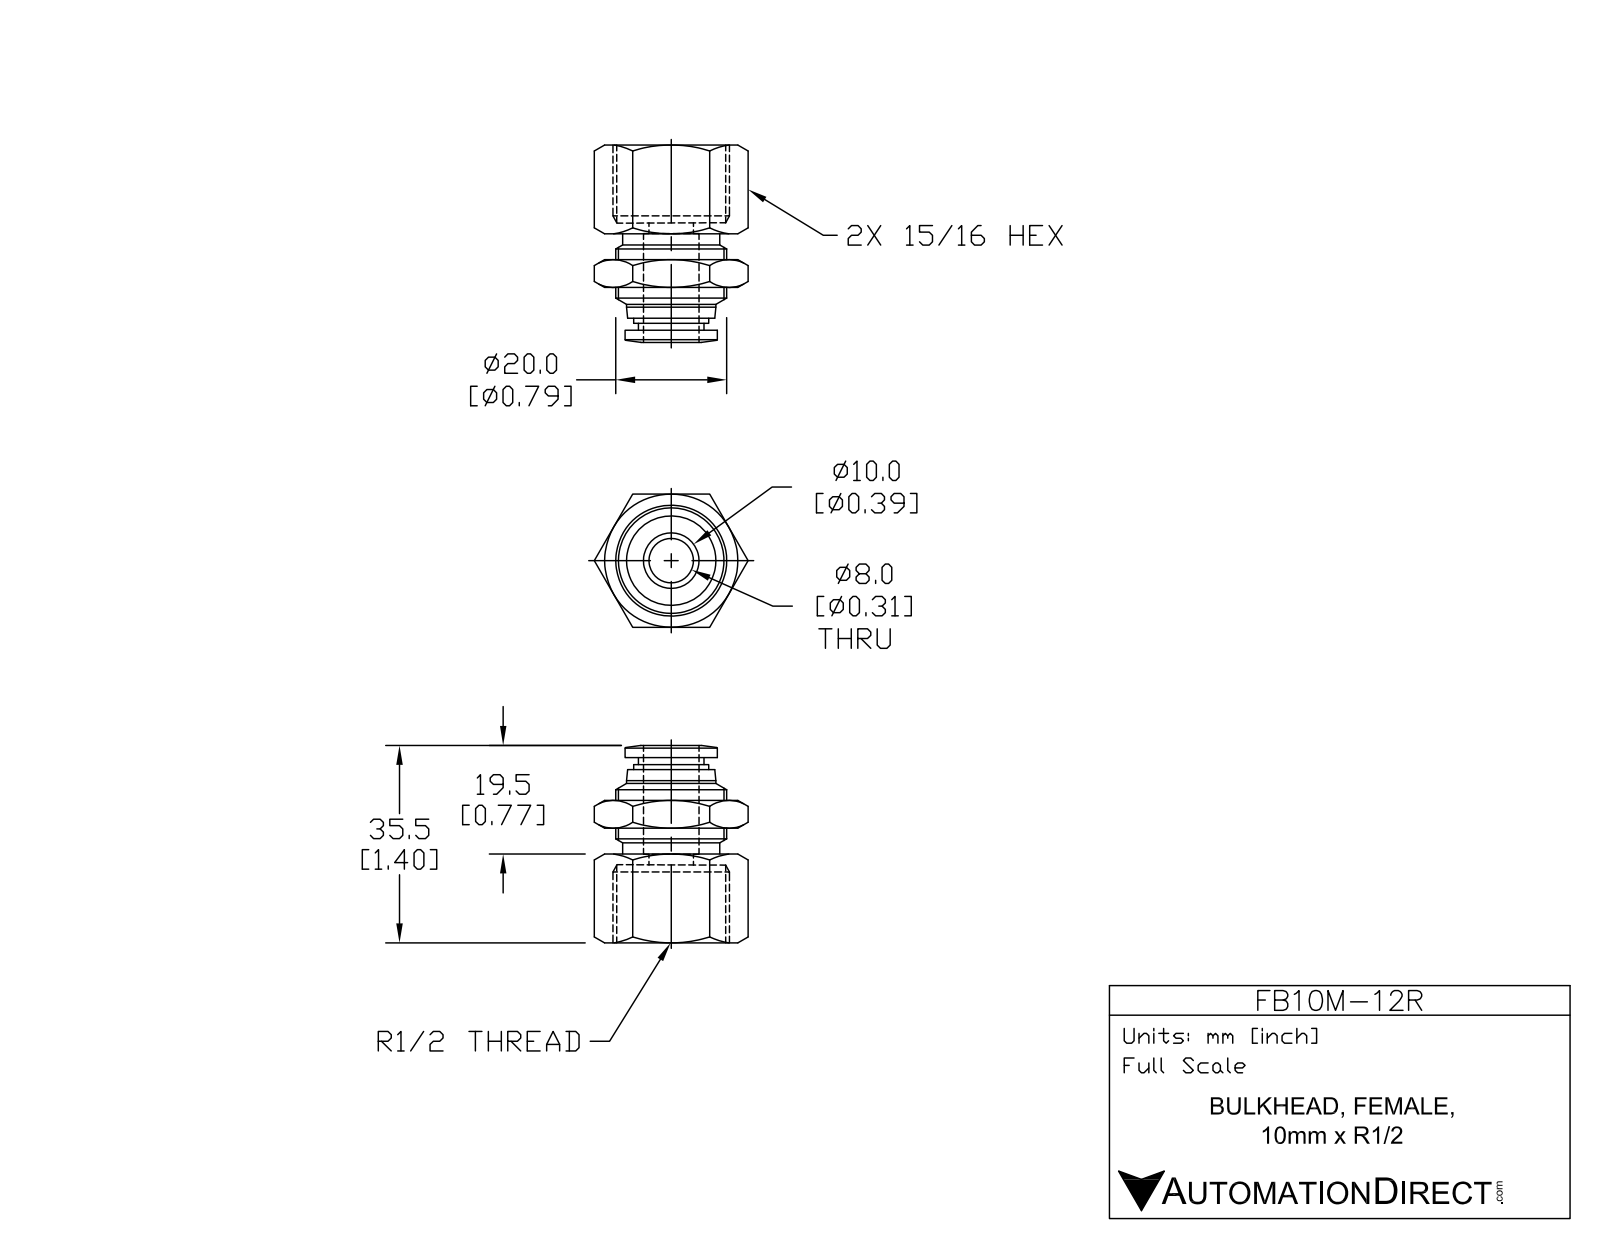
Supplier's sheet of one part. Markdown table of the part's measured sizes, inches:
| quantity | value |
| --- | --- |
| part name | FB10M-12R |
| STEP written by | SolidWorks 2015 (AUTOMOTIVE_DESIGN) |
| units | inches |
| bodies | 1 solid, 82 faces (22 planar, 18 cylindrical, 42 other) |
| overall size | 1.4 × 1.091 × 0.945 |
| volume | 0.455 in³ |
| surface area | 8.538 in² |
| round holes (diameter × count) | 0.315 × 1, 0.406 × 1 |
| round bosses / shafts (diameter × count) | 0.787 × 1, 0.689 × 1, 0.654 × 1, 0.634 × 1, 0.531 × 1, 0.465 × 1 |
| main face-to-face distances | 0.945, 0.079, 0.258, 0.18, 0.455, 0.376, 0.197, 0.551, 0.63, 0.809 |
